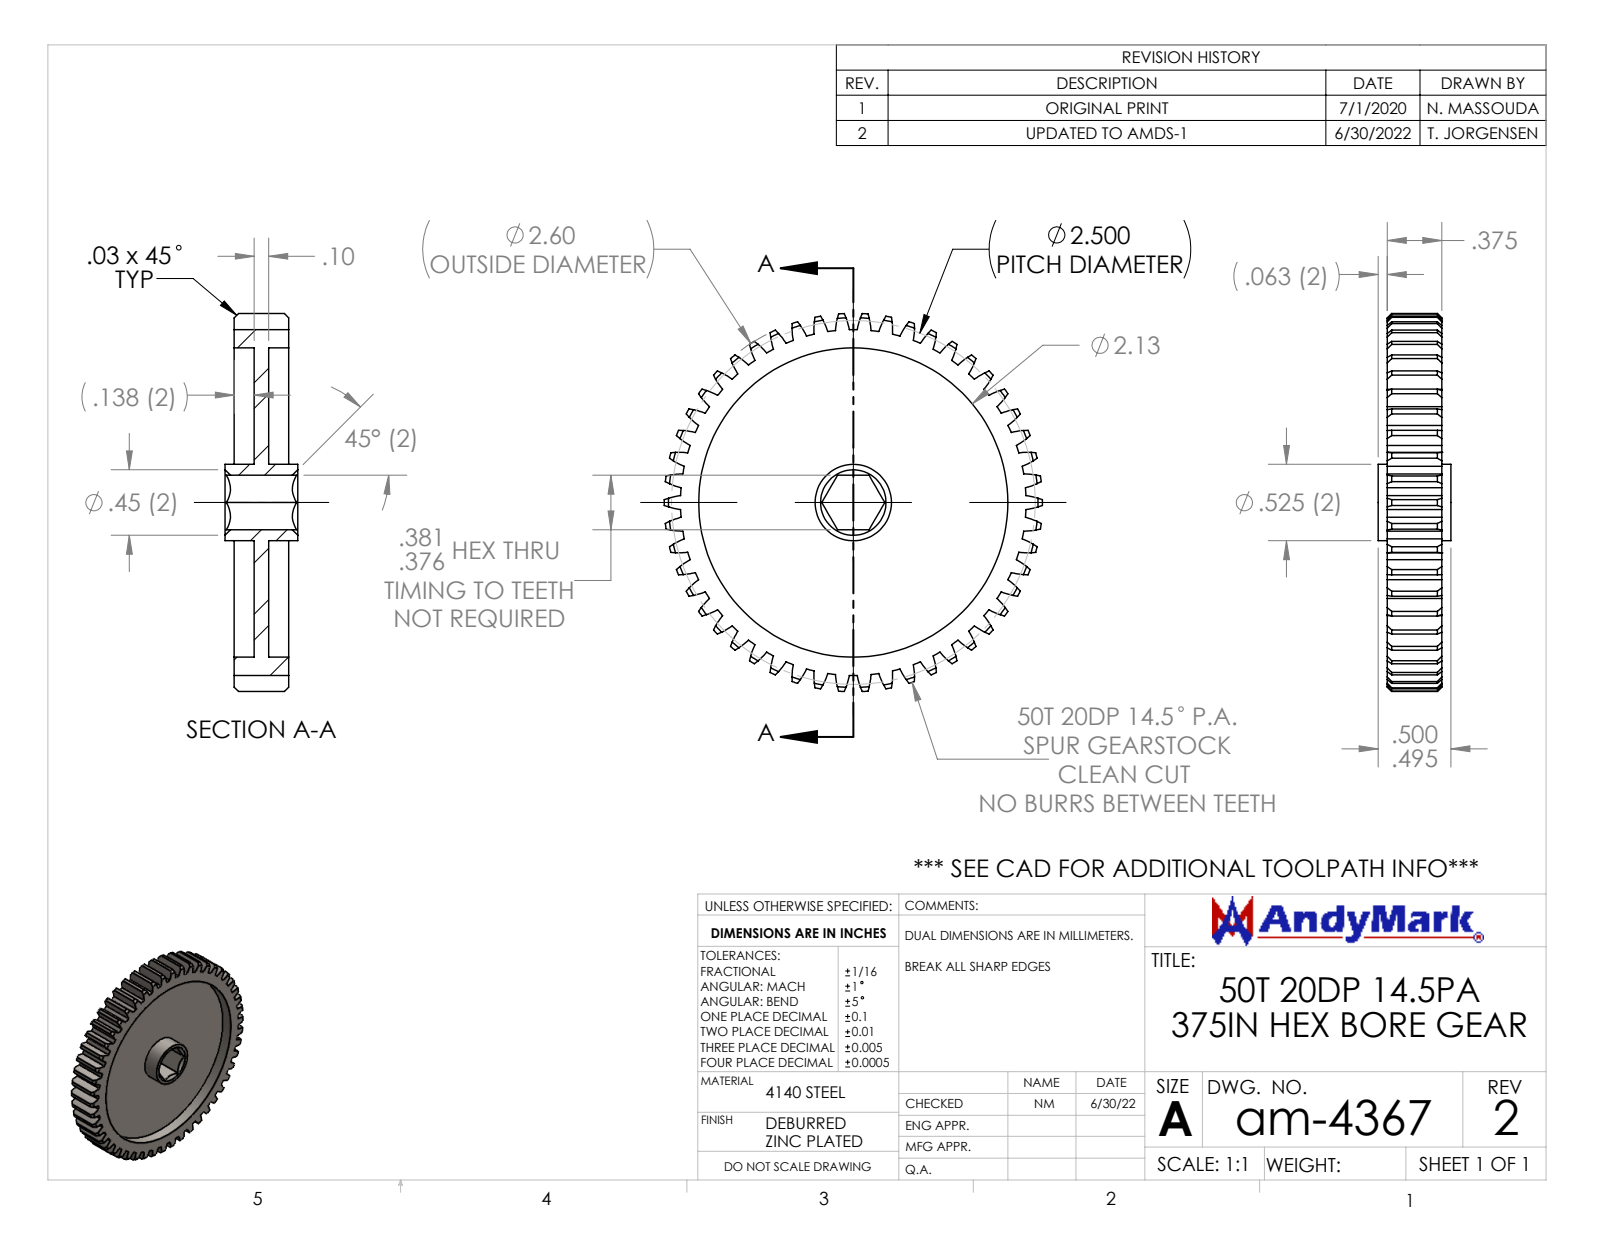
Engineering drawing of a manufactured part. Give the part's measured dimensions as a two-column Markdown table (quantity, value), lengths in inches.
| quantity | value |
| --- | --- |
| part name | am-4367 50T 20DP 375hex 375 FW |
| STEP written by | SolidWorks 2022 (CONFIG_CONTROL_DESIGN) |
| units | inches |
| bodies | 1 solid, 329 faces (12 planar, 213 cylindrical, 104 other) |
| overall size | 2.6 × 2.597 × 0.5 |
| volume | 0.862 in³ |
| surface area | 18.5 in² |
| round holes (diameter × count) | 2.125 × 1 |
| round bosses / shafts (diameter × count) | 0.525 × 1 |
| partial cylindrical surfaces (radius × count) | 0.5 × 100, 1.188 × 1, 1.3 × 1 |
| main face-to-face distances | 0.1, 0.137, 0.237, 0.375, 0.238, 0.138, 0.375, 0.2, 0.3, 0.063 |
